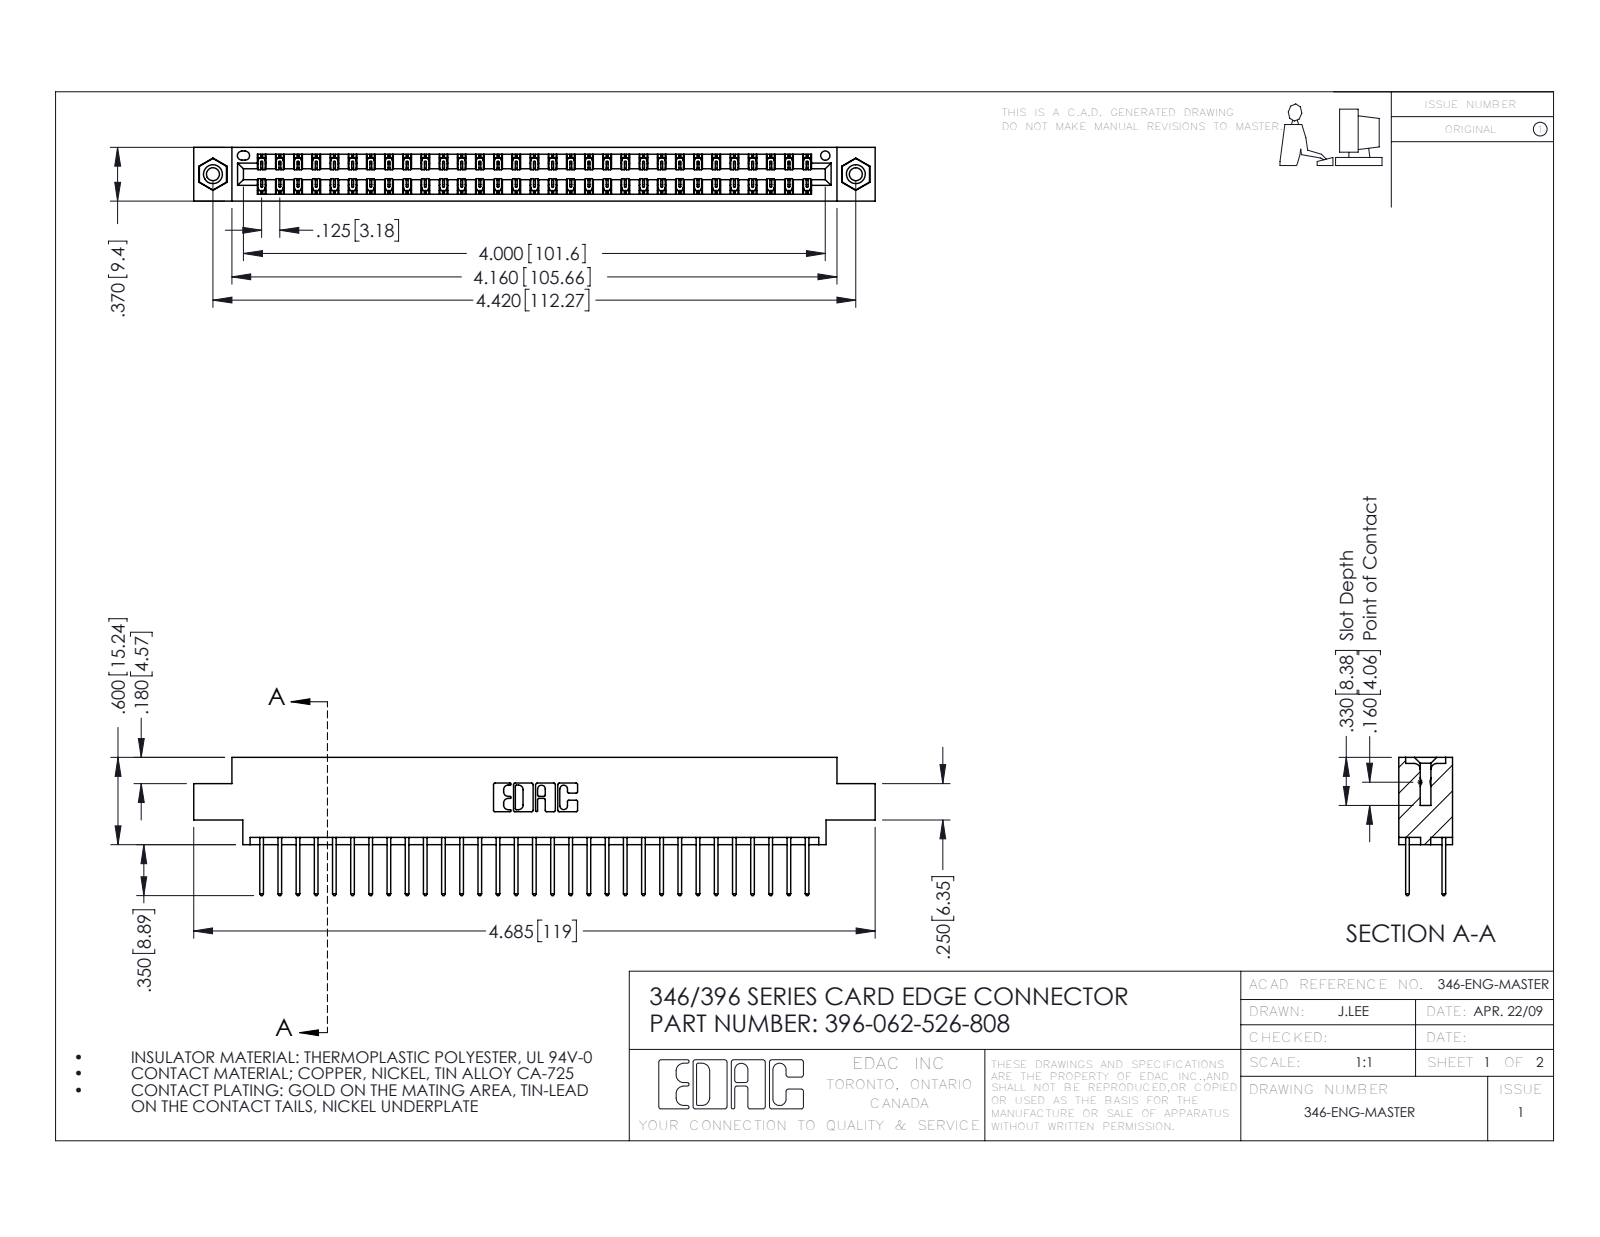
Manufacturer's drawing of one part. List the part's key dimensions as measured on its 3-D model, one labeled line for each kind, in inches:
Part name (STEP PRODUCT): 346 Part_0.170 Offset - 0.156 Dia-TI; 396-062-526-808; 345-250-001_345-250-003-102; 345-292-001_345-293-126
STEP written by: SolidWorks 2016 (CONFIG_CONTROL_DESIGN)
Units: inches
Bodies: 65 solids, 3410 faces (2282 planar, 1112 cylindrical, 16 other)
Overall size (bounding box): 4.685 × 0.95 × 0.37
Volume: 0.699 in³ · Surface area: 25.16 in²
Round holes (diameter × count): ⌀0.089 ×2, ⌀0.125 ×2, ⌀0.156 ×2, ⌀0.064 ×1
Round bosses / shafts (diameter × count): ⌀0.155 ×2
Partial cylindrical surfaces — rounded edges, fillets, slot ends (radius × count): R0.006 ×93, R0.01 ×62, R0.01 ×22, R0.007 ×6, R0.031 ×6, R0.026 ×3, R0.014 ×2, R0.022 ×2
Main face-to-face distances: 0.048, 0.322, 0.25, 0.37, 0.072, 0.298, 0.025, 0.275, 0.222, 0.148
Hole centre spacings: 0.246, 4.212, 4.42
